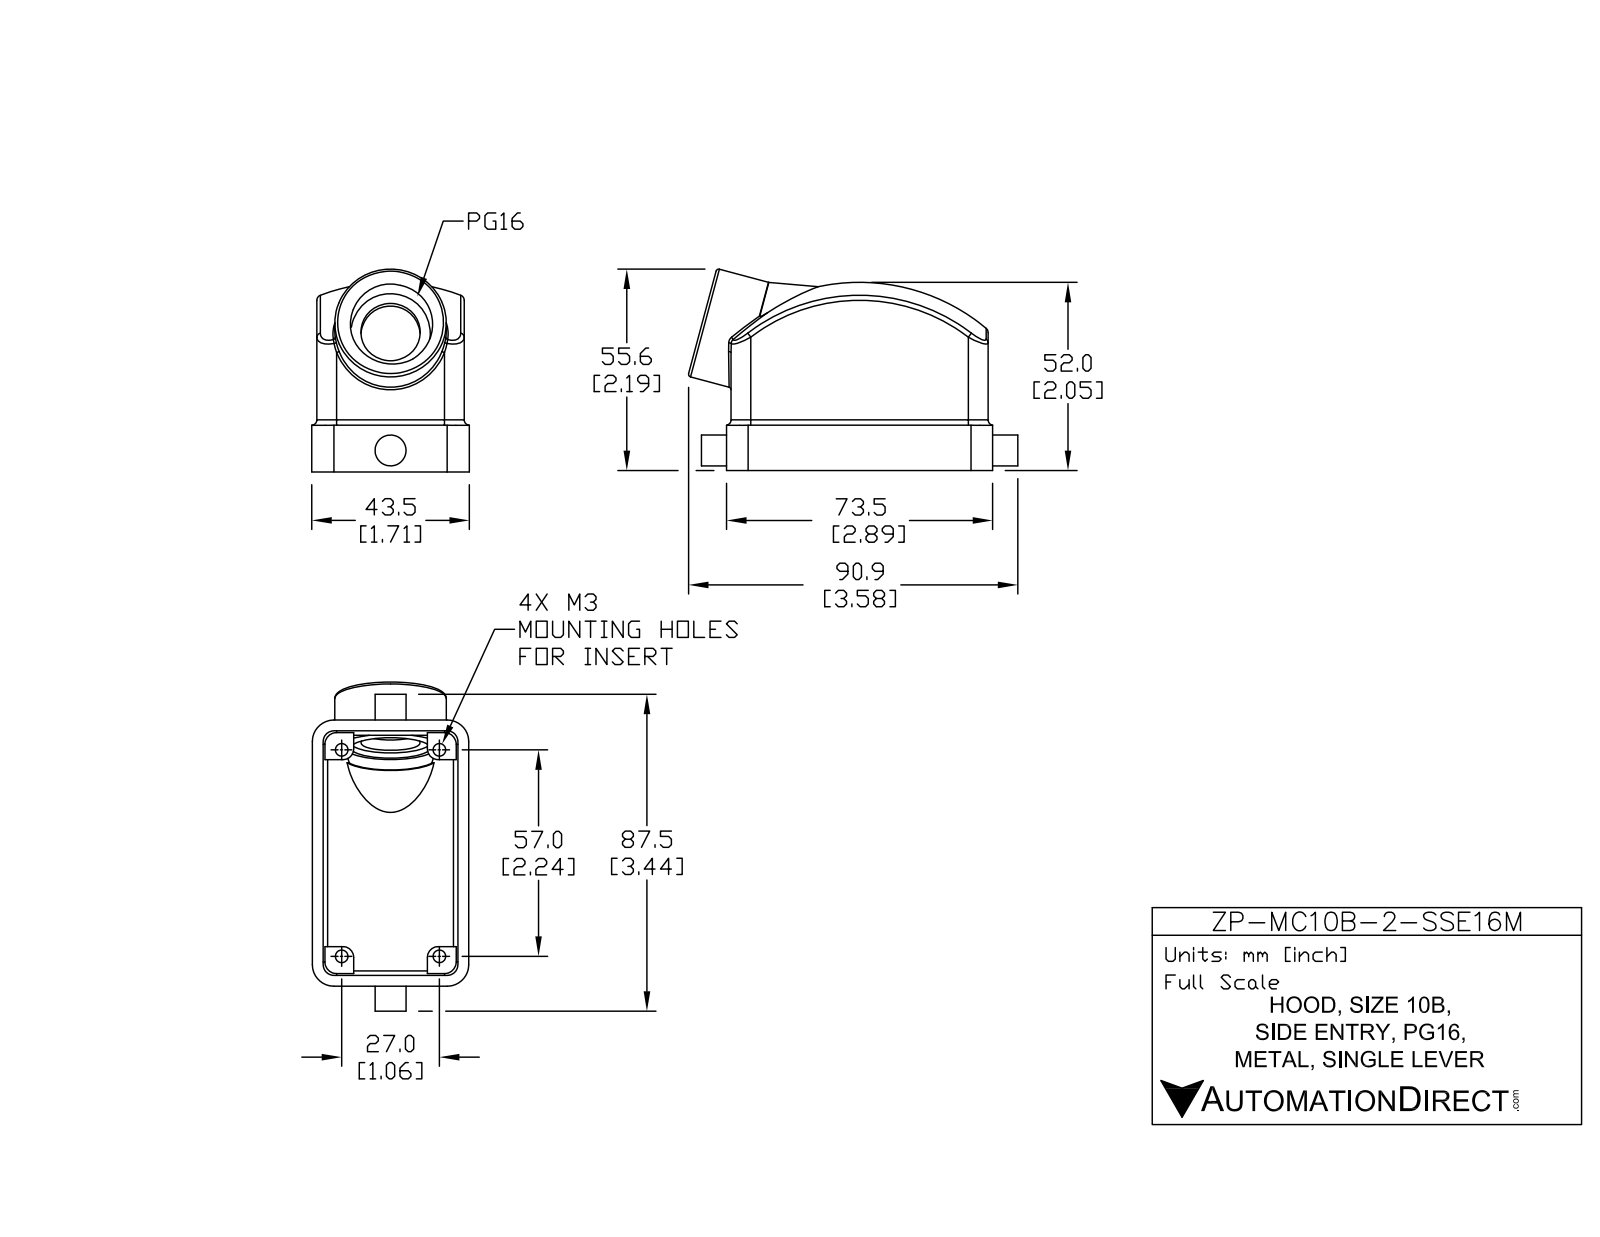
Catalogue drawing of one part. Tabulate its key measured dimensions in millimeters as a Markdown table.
| quantity | value |
| --- | --- |
| part name | ZP-MC10B-2-SSE16M |
| STEP written by | SolidWorks 2011 (AUTOMOTIVE_DESIGN) |
| units | millimeters |
| bodies | 4 solids, 127 faces (46 planar, 45 cylindrical, 36 other) |
| overall size | 91.58 × 56.43 × 43.5 |
| volume | 43 383 mm³ |
| surface area | 29 084 mm² |
| round holes (diameter × count) | 3.5 × 4, 16.5 × 1, 22 × 1 |
| round bosses / shafts (diameter × count) | 31 × 1, 8.6 × 1 |
| partial cylindrical surfaces (radius × count) | 3 × 8, 1.5 × 4, 4.5 × 4, 5.5 × 4, 6 × 4, 12.5 × 1, 14.75 × 1 |
| main face-to-face distances | 3, 1.25, 38, 39.25, 4.25, 1.75, 41, 42.25, 35, 40.5 |
| hole center spacings | 26.5, 58, 63.77 |
